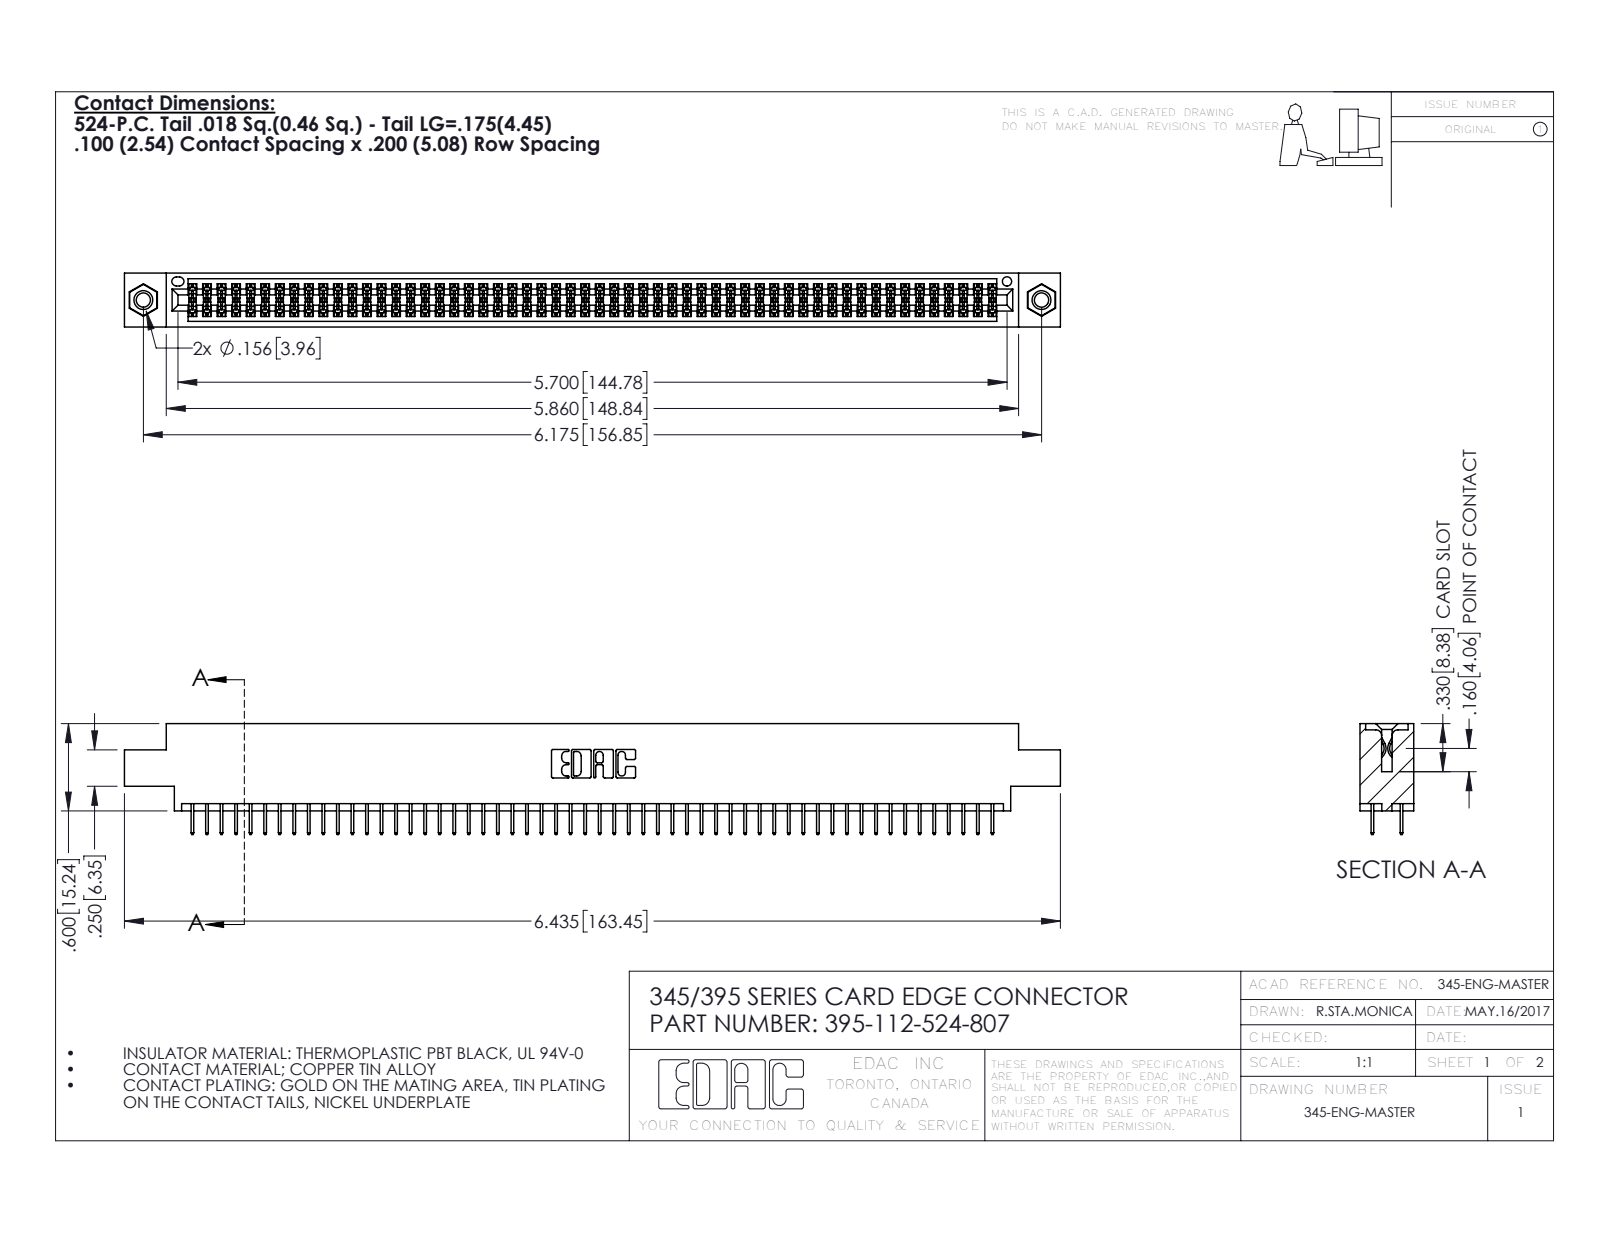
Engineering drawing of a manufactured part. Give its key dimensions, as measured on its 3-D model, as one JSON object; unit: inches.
{"part_name": "345-250-001_345-250-005-103; 345-292-001_345-293-124; 395-112-524-807; 345 Part_0.170 Offset - 0.156 Dia-TI", "step_written_by": "SolidWorks 2016 (CONFIG_CONTROL_DESIGN)", "units": "inches", "bodies": {"solids": 115, "faces": 6238, "planar": 4484, "cylindrical": 1738, "other": 16}, "overall_size": [6.435, 0.762, 0.37], "volume_in3": 0.959, "surface_area_in2": 35.99, "round_holes": [[0.098, 2], [0.125, 2], [0.156, 2], [0.064, 1]], "round_bosses_or_shafts": [[0.155, 2]], "partial_cylinders_radius": [[0.006, 168], [0.01, 22], [0.007, 6], [0.031, 6], [0.026, 3], [0.014, 2], [0.019, 2], [0.022, 2]], "face_to_face_distances": [0.072, 0.298, 0.37, 0.2, 0.098, 0.272, 0.025, 0.225, 0.072, 0.175], "hole_center_spacings": [0.27, 5.939, 6.175]}
